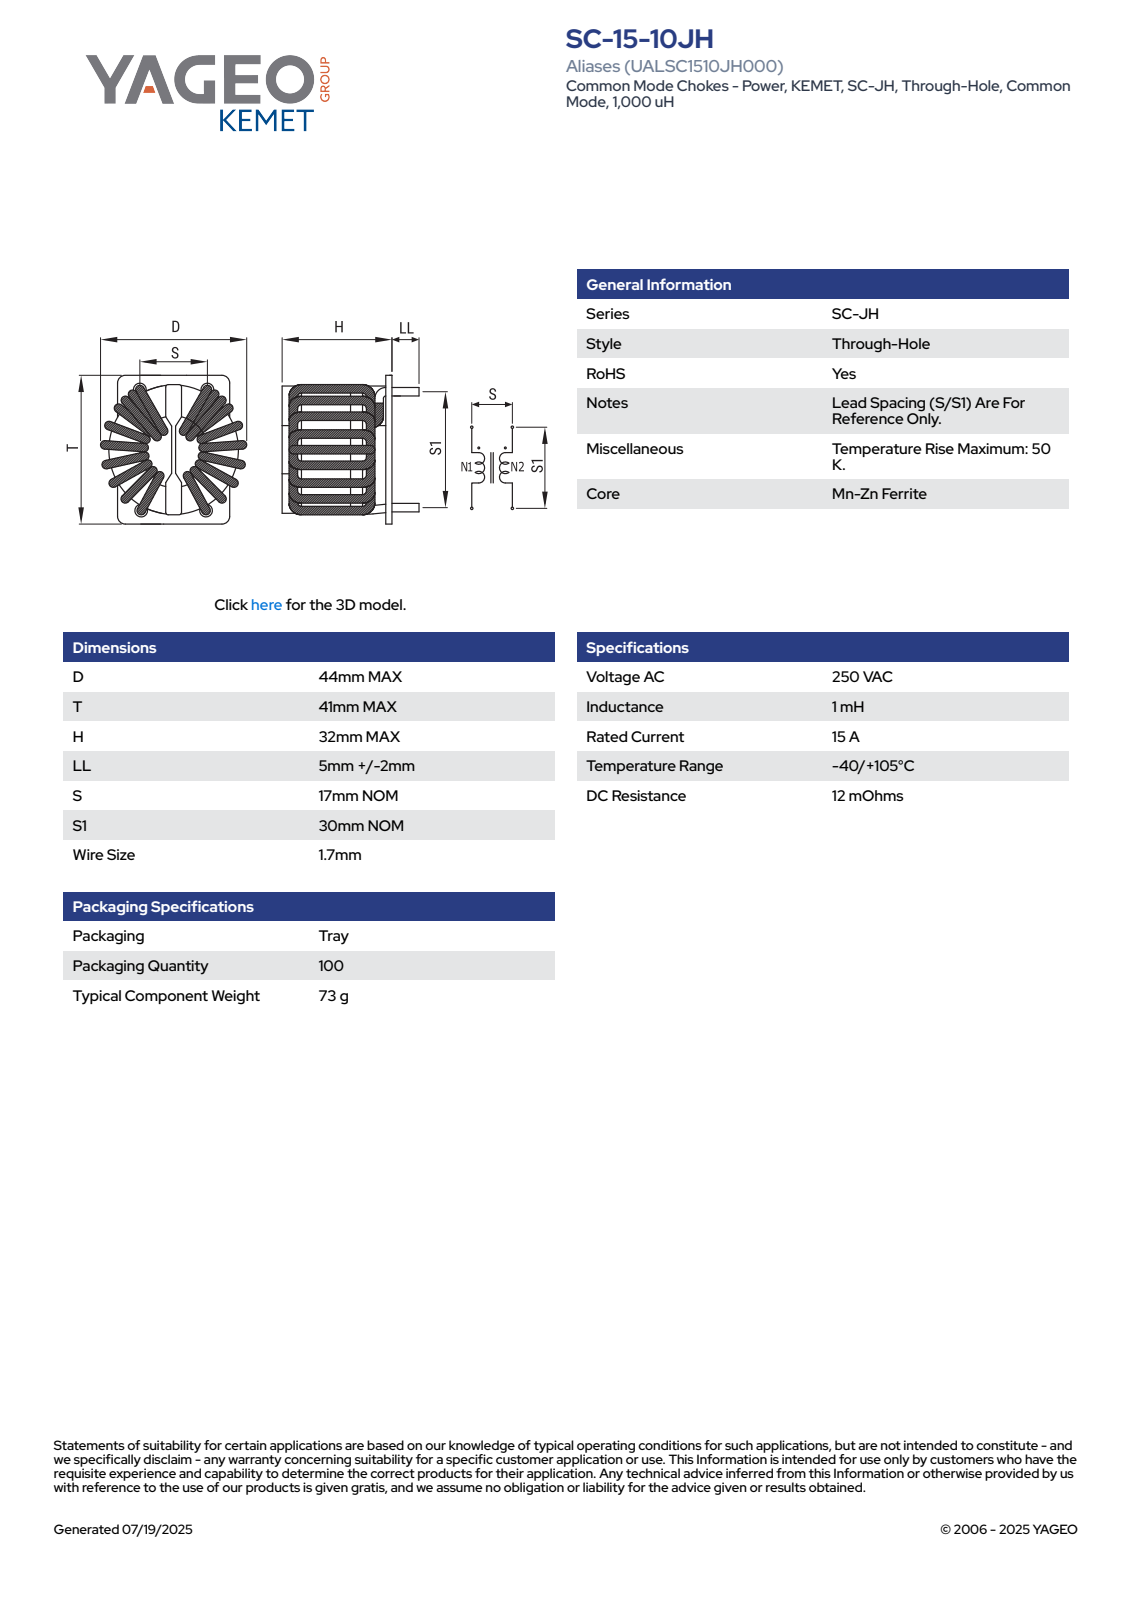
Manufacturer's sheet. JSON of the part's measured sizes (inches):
{"part_name": "SC-15-10JH", "step_written_by": "SolidWorks 2018 (AUTOMOTIVE_DESIGN)", "units": "inches", "bodies": {"solids": 1, "faces": 518, "planar": 240, "cylindrical": 164, "other": 114}, "overall_size": [1.732, 1.614, 1.457], "volume_in3": 1.863, "surface_area_in2": 22.25, "round_holes": [[0.087, 4]], "round_bosses_or_shafts": [[0.067, 12]], "partial_cylinders_radius": [[0.02, 30], [0.033, 28], [0.031, 8], [0.236, 4], [0.016, 2], [0.039, 2], [0.26, 1], [0.346, 1]], "face_to_face_distances": [0.126, 1.071, 0.299, 0.173, 1.197, 0.898, 0.051, 0.039, 0.094, 0.043], "hole_center_spacings": [0.669, 1.181, 1.357]}
